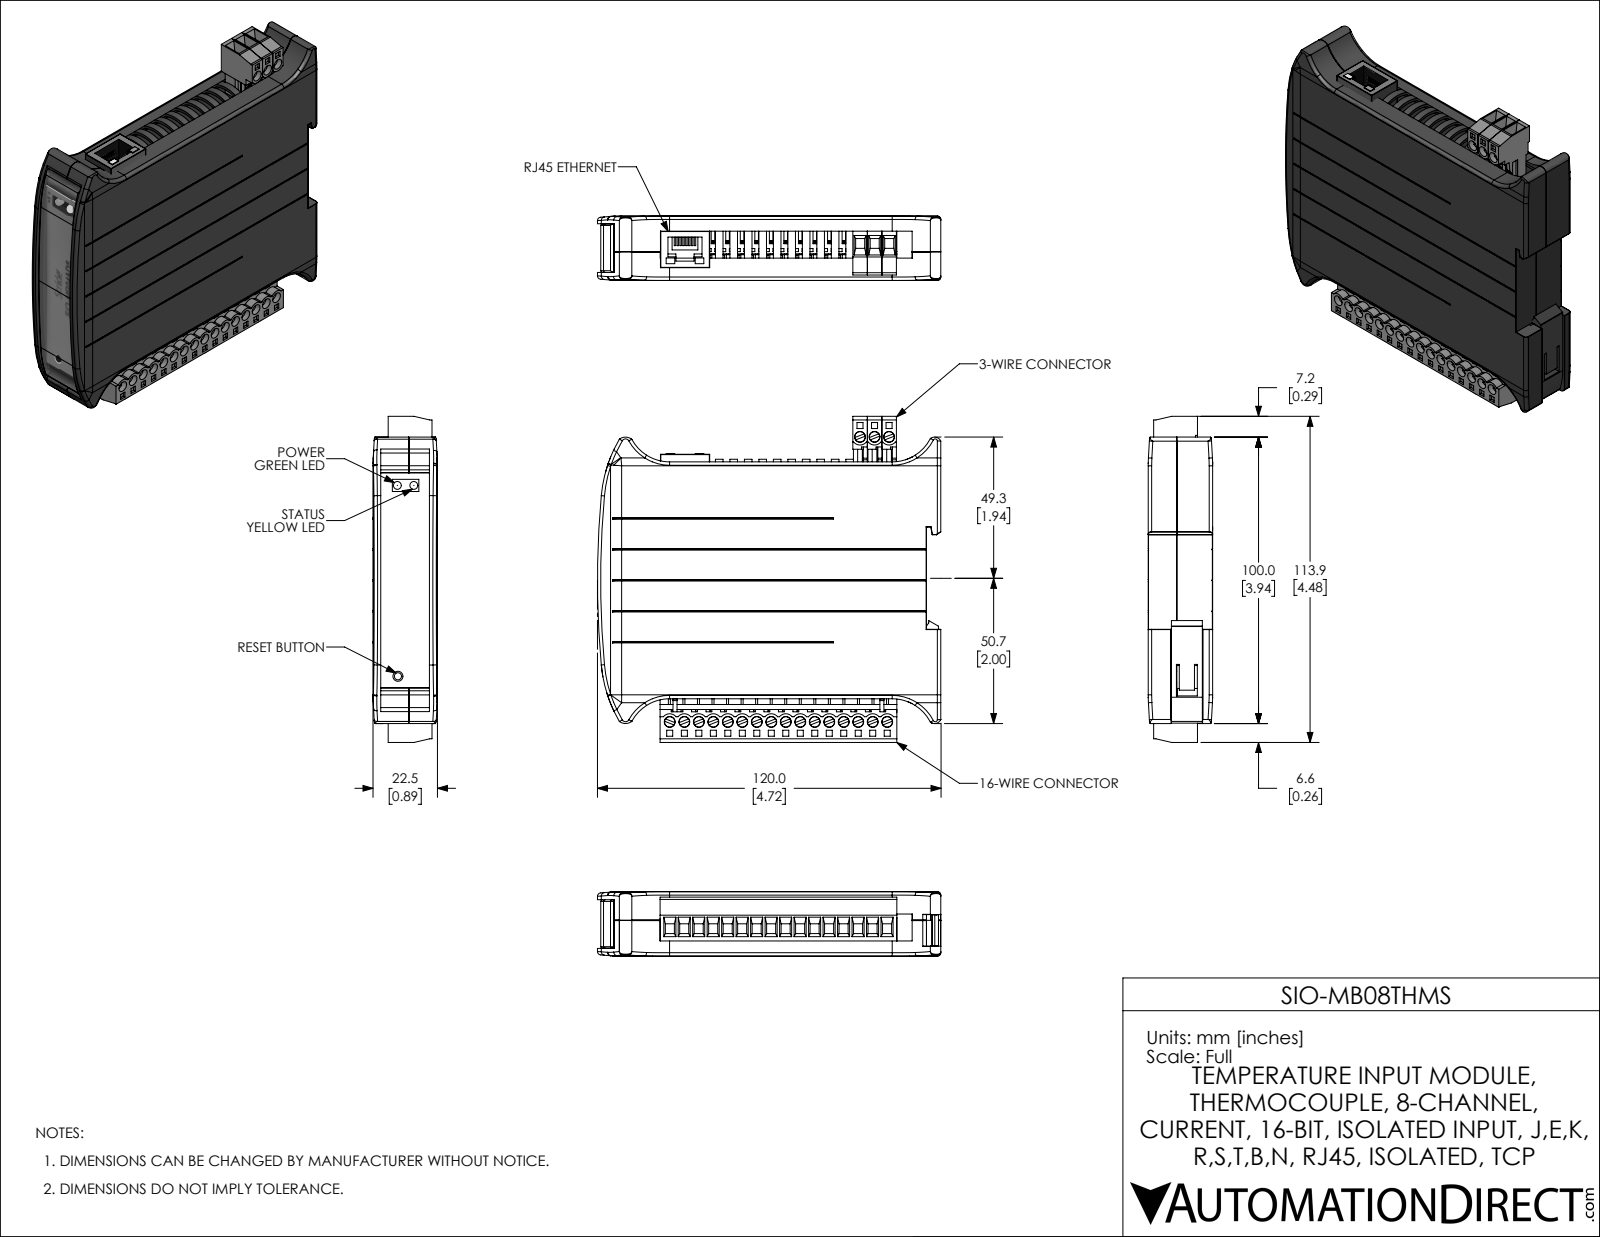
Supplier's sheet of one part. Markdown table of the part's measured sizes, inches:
| quantity | value |
| --- | --- |
| part name | SIO-MB04ADS |
| STEP written by | SolidWorks 2019 (AUTOMOTIVE_DESIGN) |
| units | inches |
| bodies | 21 solids, 2737 faces (2081 planar, 435 cylindrical, 221 other) |
| overall size | 4.689 × 4.482 × 0.886 |
| volume | 4.888 in³ |
| surface area | 133.1 in² |
| round holes (diameter × count) | 0.15 × 19, 0.094 × 2, 0.138 × 1 |
| round bosses / shafts (diameter × count) | 0.142 × 19, 0.079 × 16, 0.108 × 2, 0.154 × 1, 0.098 × 1, 0.091 × 1 |
| partial cylindrical surfaces (radius × count) | 0.004 × 104, 0.112 × 35, 0.01 × 20, 0.113 × 19, 0.047 × 12, 1.988 × 9, 0.005 × 8, 0.008 × 6 |
| main face-to-face distances | 0.059, 0.827, 0.886, 0.768, 0.618, 0.209, 0.15, 0.283, 0.677, 0.335 |
| hole center spacings | 0.199, 0.398, 0.598, 0.797, 0.996, 1.195, 1.394, 1.594 |
